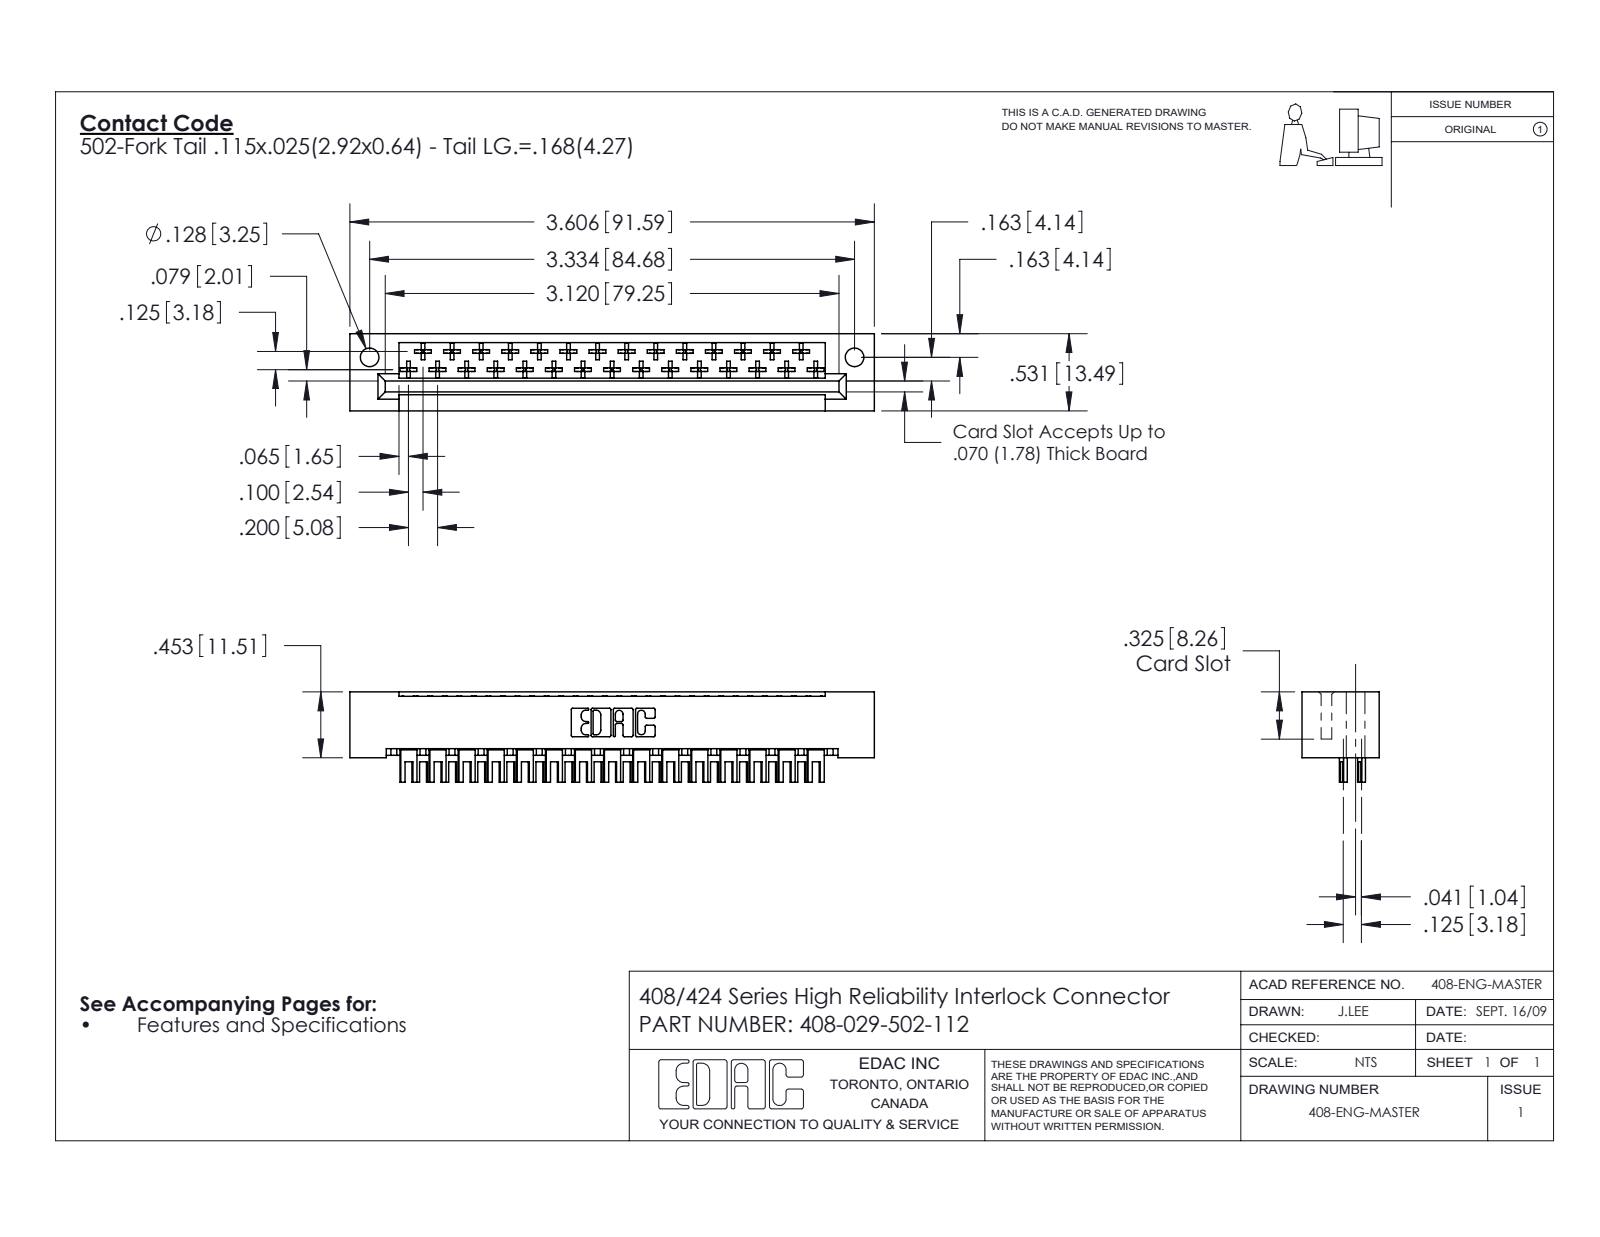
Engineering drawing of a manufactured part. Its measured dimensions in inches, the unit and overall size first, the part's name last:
Units: inches
Overall size (bounding box): 3.606 × 0.621 × 0.531
Round holes (diameter × count): ⌀0.128 ×2
Partial cylindrical surfaces — rounded edges, fillets, slot ends (radius × count): R0.01 ×174, R0.02 ×31, R0.01 ×22, R0.007 ×6, R0.031 ×6, R0.026 ×3
Main face-to-face distances: 0.531, 0.025, 0.4, 0.1, 0.125, 0.025, 0.235, 0.259, 0.272, 0.296
Hole centre spacings: 3.334
Volume: 0.647 in³ · Surface area: 19.53 in²
Bodies: 30 solids, 1664 faces (1268 planar, 280 cylindrical, 116 other)
Part name (STEP PRODUCT): 408-290-001_408-290-102; 408-029-502-112; 408 Part_029 - 1
STEP written by: SolidWorks 2016 (CONFIG_CONTROL_DESIGN)
